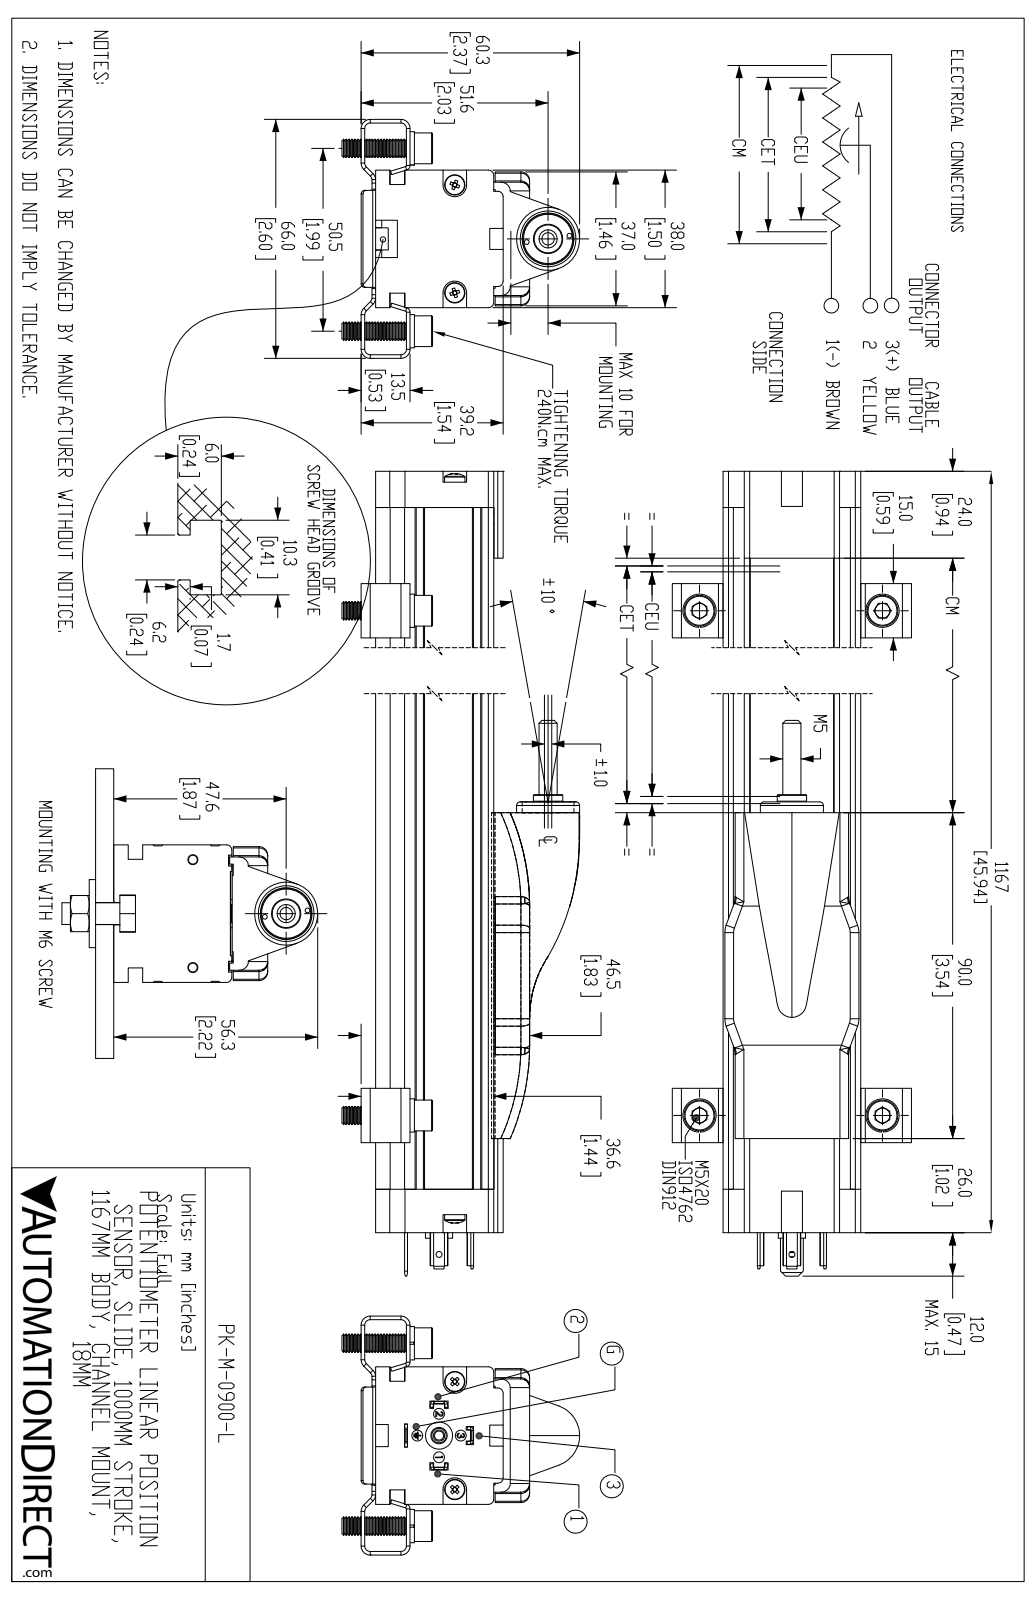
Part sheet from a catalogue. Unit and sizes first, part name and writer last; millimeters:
Units: millimetres
Overall size (bounding box): 1179 × 66 × 65.6
Round holes (diameter × count): ⌀5.1 ×6, ⌀3 ×5, ⌀5.3 ×3, ⌀1.3 ×2, ⌀1.5 ×2, ⌀1.7 ×2, ⌀2.6 ×2, ⌀2.7 ×2, ⌀3.3 ×2, ⌀1.6 ×1, ⌀2.5 ×1, ⌀4 ×1
Round bosses / shafts (diameter × count): ⌀5 ×9, ⌀9.2 ×6, ⌀8.5 ×6, ⌀5.6 ×2, ⌀3 ×2, ⌀2.5 ×2, ⌀17.4 ×1, ⌀14 ×1
Partial cylindrical surfaces — rounded edges, fillets, slot ends (radius × count): R1 ×40, R1.5 ×12, R2.6 ×12, R2.5 ×8, R6 ×8, R0.6 ×6, R0.8 ×6, R1.6 ×6
Main face-to-face distances: 32.2, 4, 32.3, 38, 2, 26.3, 8, 6, 26.2, 34
Hole centre spacings: 6, 8.5, 50.5, 5.9, 9.9, 12, 12.3, 13.7
Volume: 1 358 000 mm³ · Surface area: 323 700 mm²
Bodies: 32 solids, 2156 faces (935 planar, 479 cylindrical, 742 other)
Part name (STEP PRODUCT): PK-M-1000-L
STEP written by: SolidWorks 2019 (AUTOMOTIVE_DESIGN)
